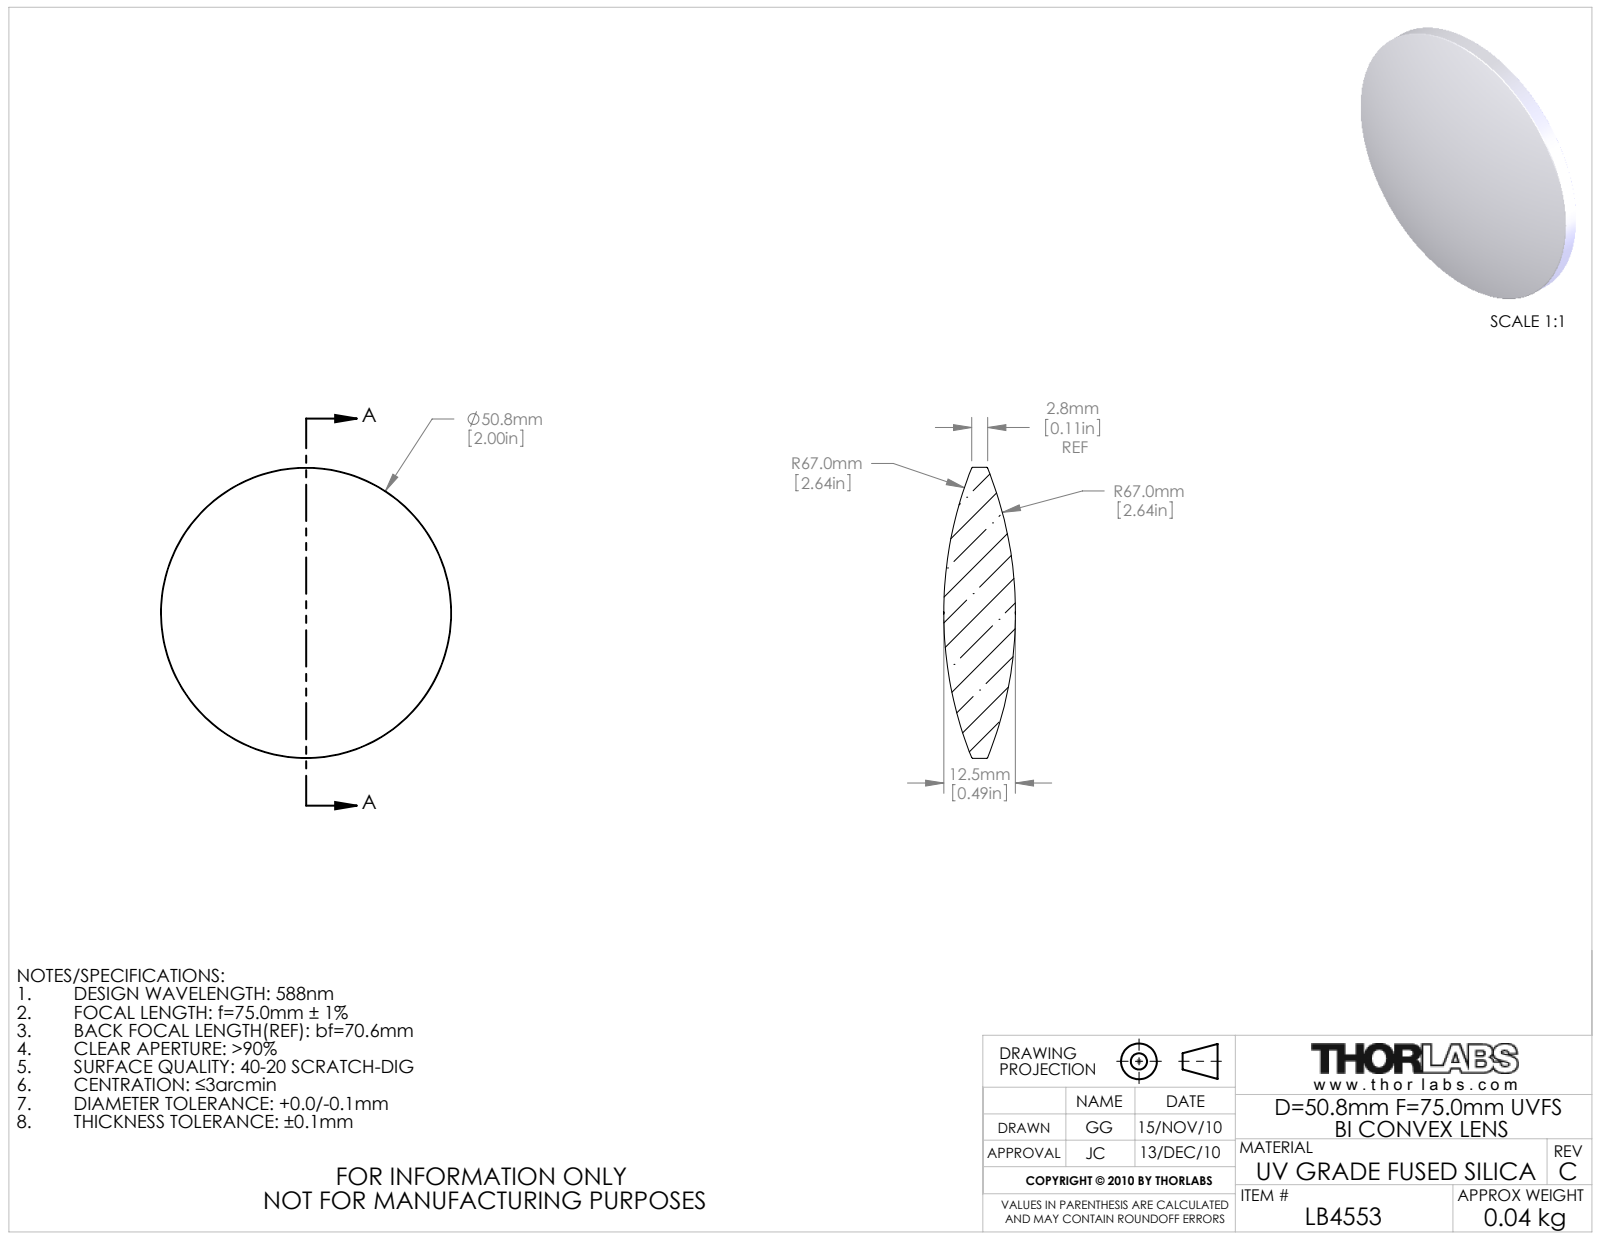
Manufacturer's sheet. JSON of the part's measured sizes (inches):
{"part_name": "3414-E0W", "step_written_by": "SolidWorks 2009 (AUTOMOTIVE_DESIGN)", "units": "inches", "bodies": {"solids": 1, "faces": 10, "planar": 0, "cylindrical": 2, "other": 8}, "overall_size": [2, 2, 0.492], "volume_in3": 0.949, "surface_area_in2": 7.163, "round_bosses_or_shafts": [[2, 1]]}
